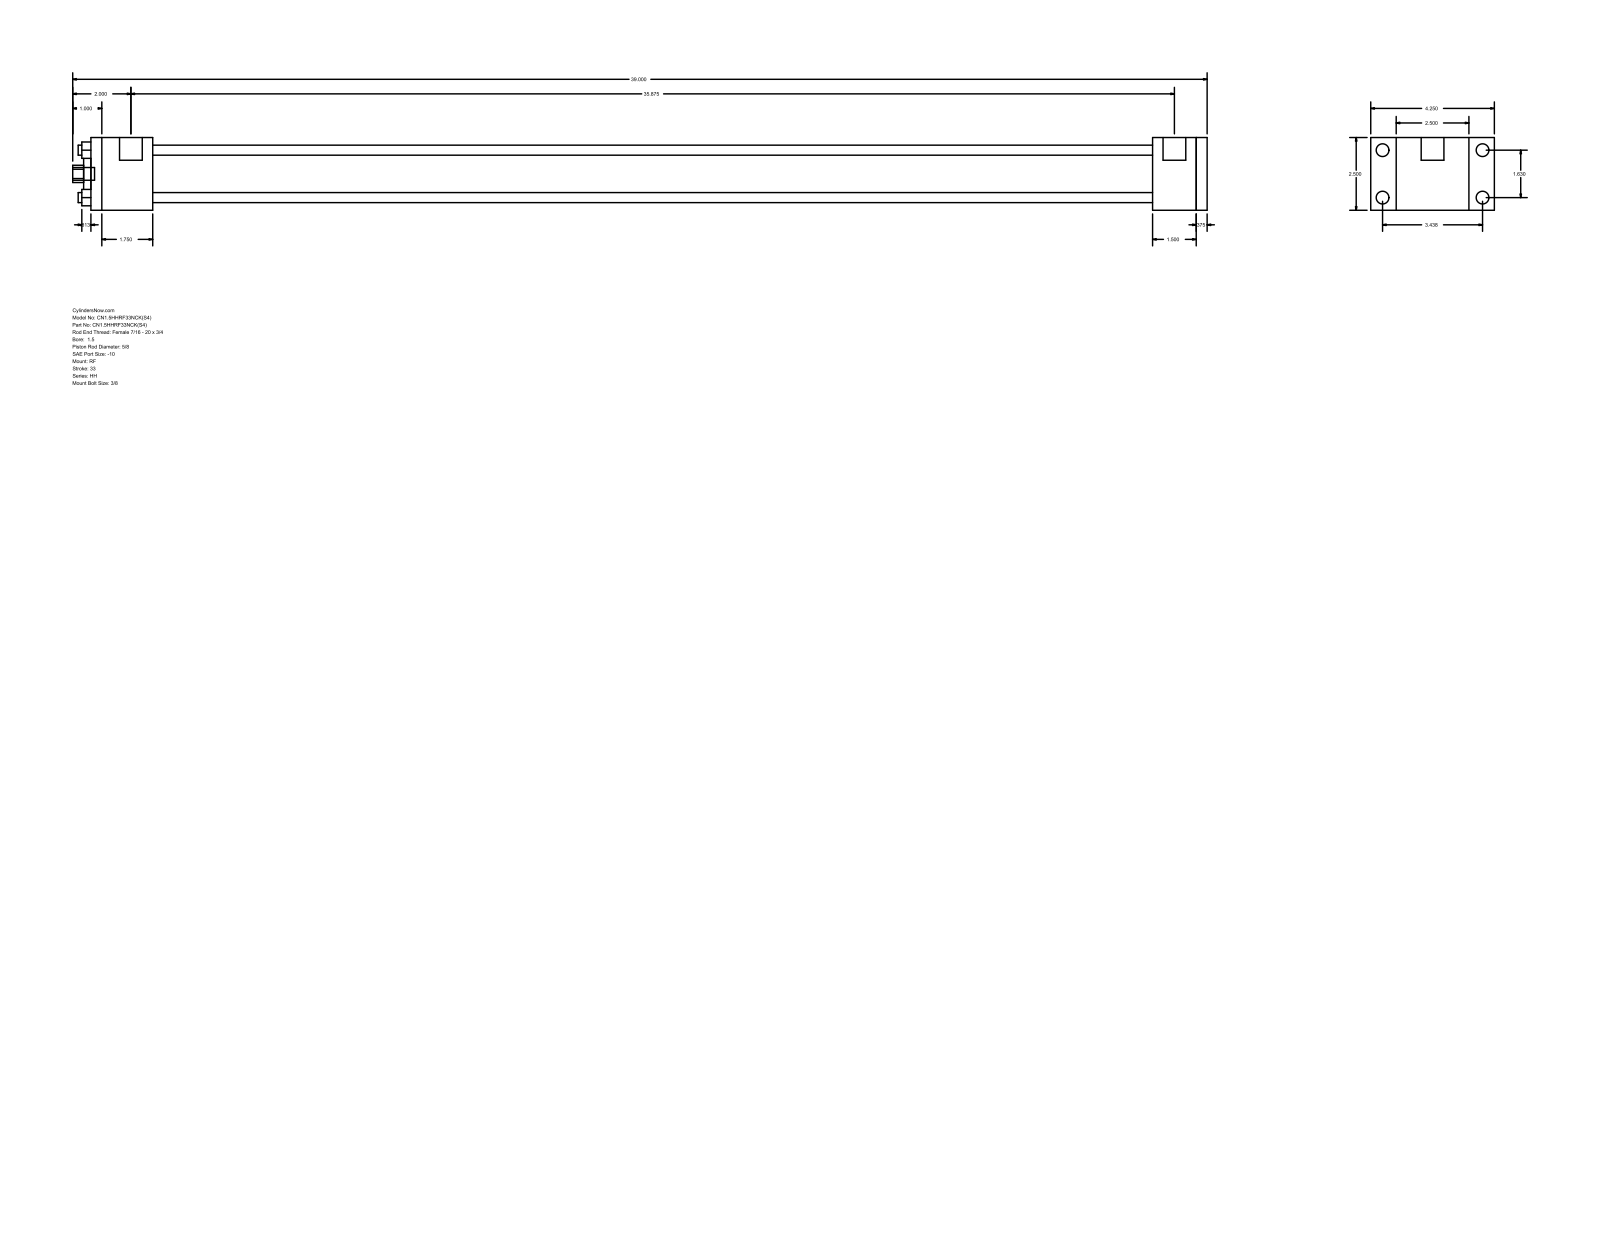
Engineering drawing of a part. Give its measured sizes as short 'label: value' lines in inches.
name: HH_RF__0150_0.625
written by: GSSL Pune (CONFIG_CONTROL_DESIGN)
unit: in
bodies: 0 solids, 92 faces (64 planar, 28 cylindrical, 0 other)
size: 39 × 4.25 × 2.5
holes: 4× ⌀0.345, 1× ⌀0.625, 1× ⌀1.125, 1× ⌀1.75
bosses: 4× ⌀0.438, 4× ⌀0.219, 2× ⌀0.781, 1× ⌀0.437
rounds: 1× R0.297
face distances: 2.5, 38.375, 0.375, 1.5, 38, 2.125, 36.5, 34.375, 35.875, 36.25
hole spacings: 1.152, 1.63, 2.305
